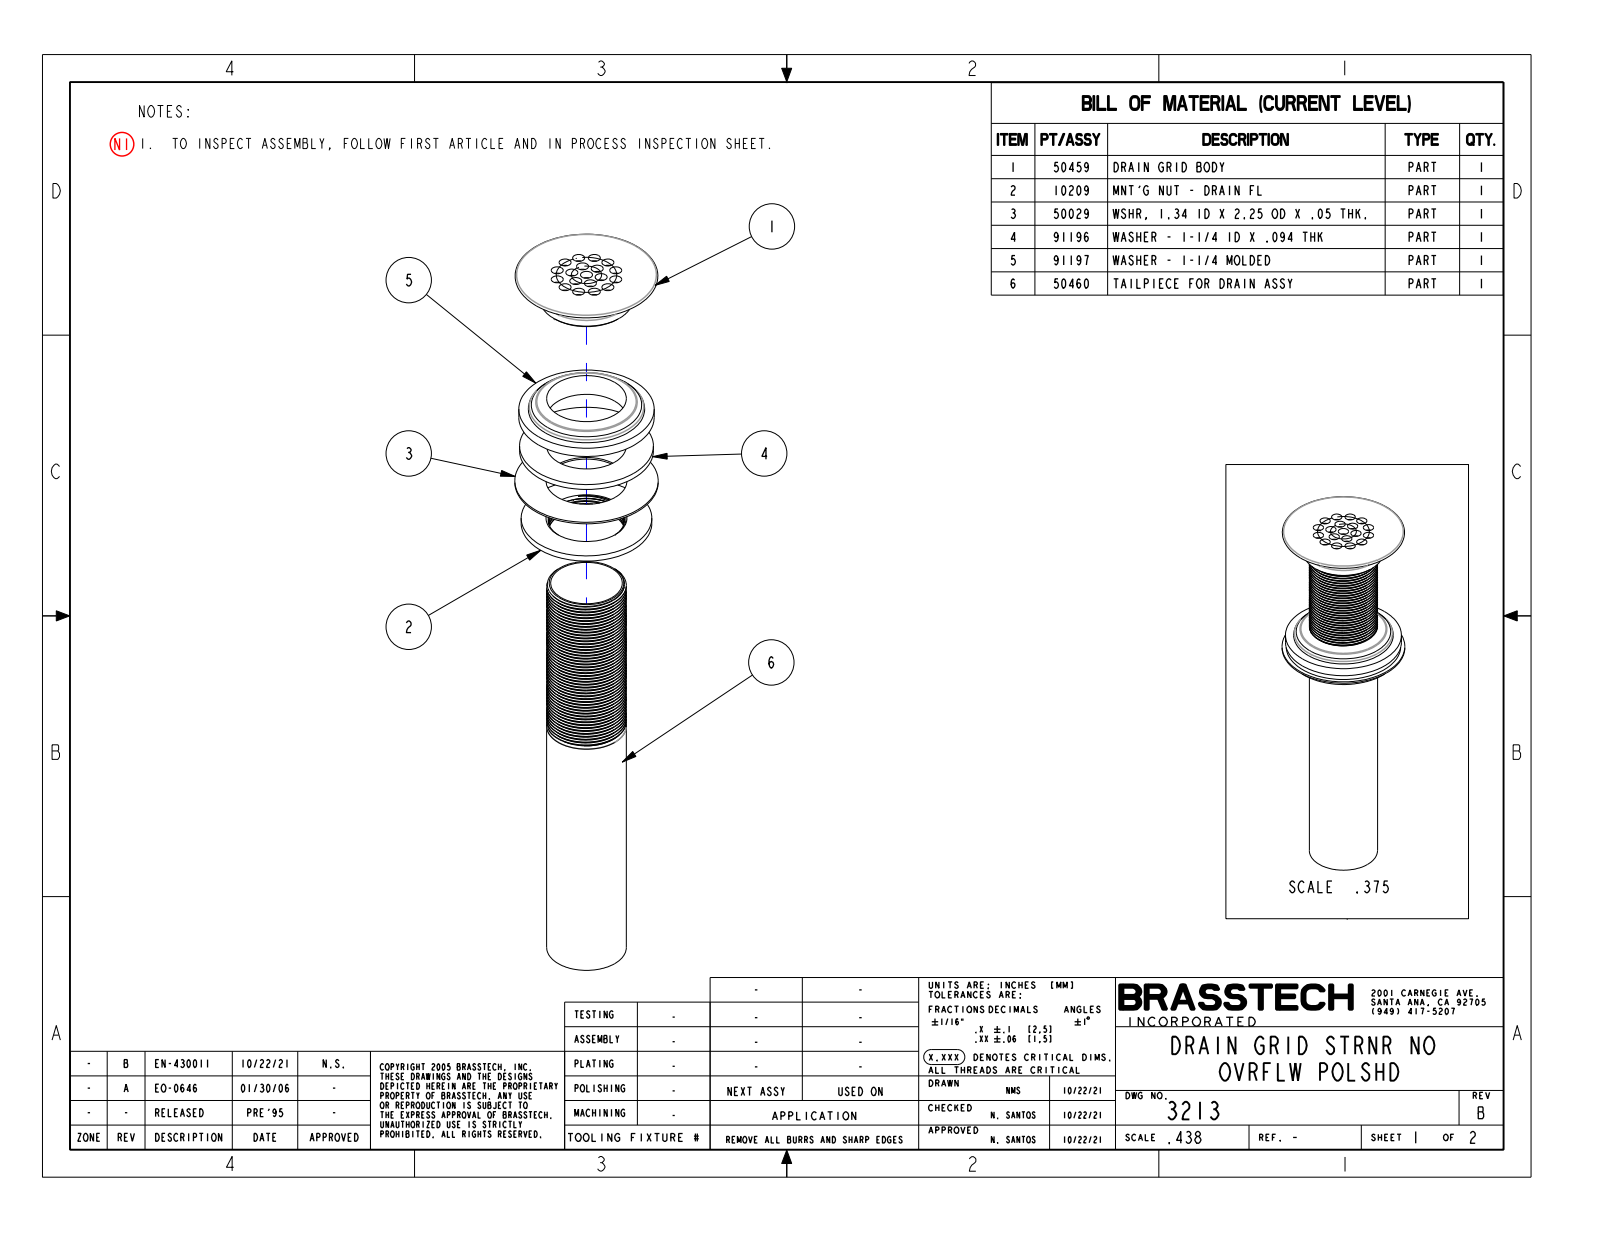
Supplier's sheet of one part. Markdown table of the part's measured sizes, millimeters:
| quantity | value |
| --- | --- |
| part name | 3213 |
| STEP written by | CREO PARAMETRIC BY PTC INC, 2018500 (CONFIG_CONTROL_DESIGN) |
| units | millimeters |
| bodies | 6 solids, 435 faces (34 planar, 319 cylindrical, 82 other) |
| overall size | 181.9 × 57.2 × 57.2 |
| volume | 135 300 mm³ |
| surface area | 95 230 mm² |
| round holes (diameter × count) | 4.8 × 19, 28.5 × 1, 30.2 × 1, 30.2 × 1, 32.3 × 1 |
| round bosses / shafts (diameter × count) | 57.2 × 1, 54 × 1, 53.3 × 1, 52.1 × 1, 37.1 × 1, 31.8 × 1, 29.5 × 1 |
| partial cylindrical surfaces (radius × count) | 3.3 × 6 |
| main face-to-face distances | 7.6, 3.8, 6.4, 59.7, 66, 3, 55.9, 7.1, 0.8, 58.9 |
| hole center spacings | 12.1, 17.1, 6, 6.2, 7.5, 10.4, 13.5, 17.6 |
